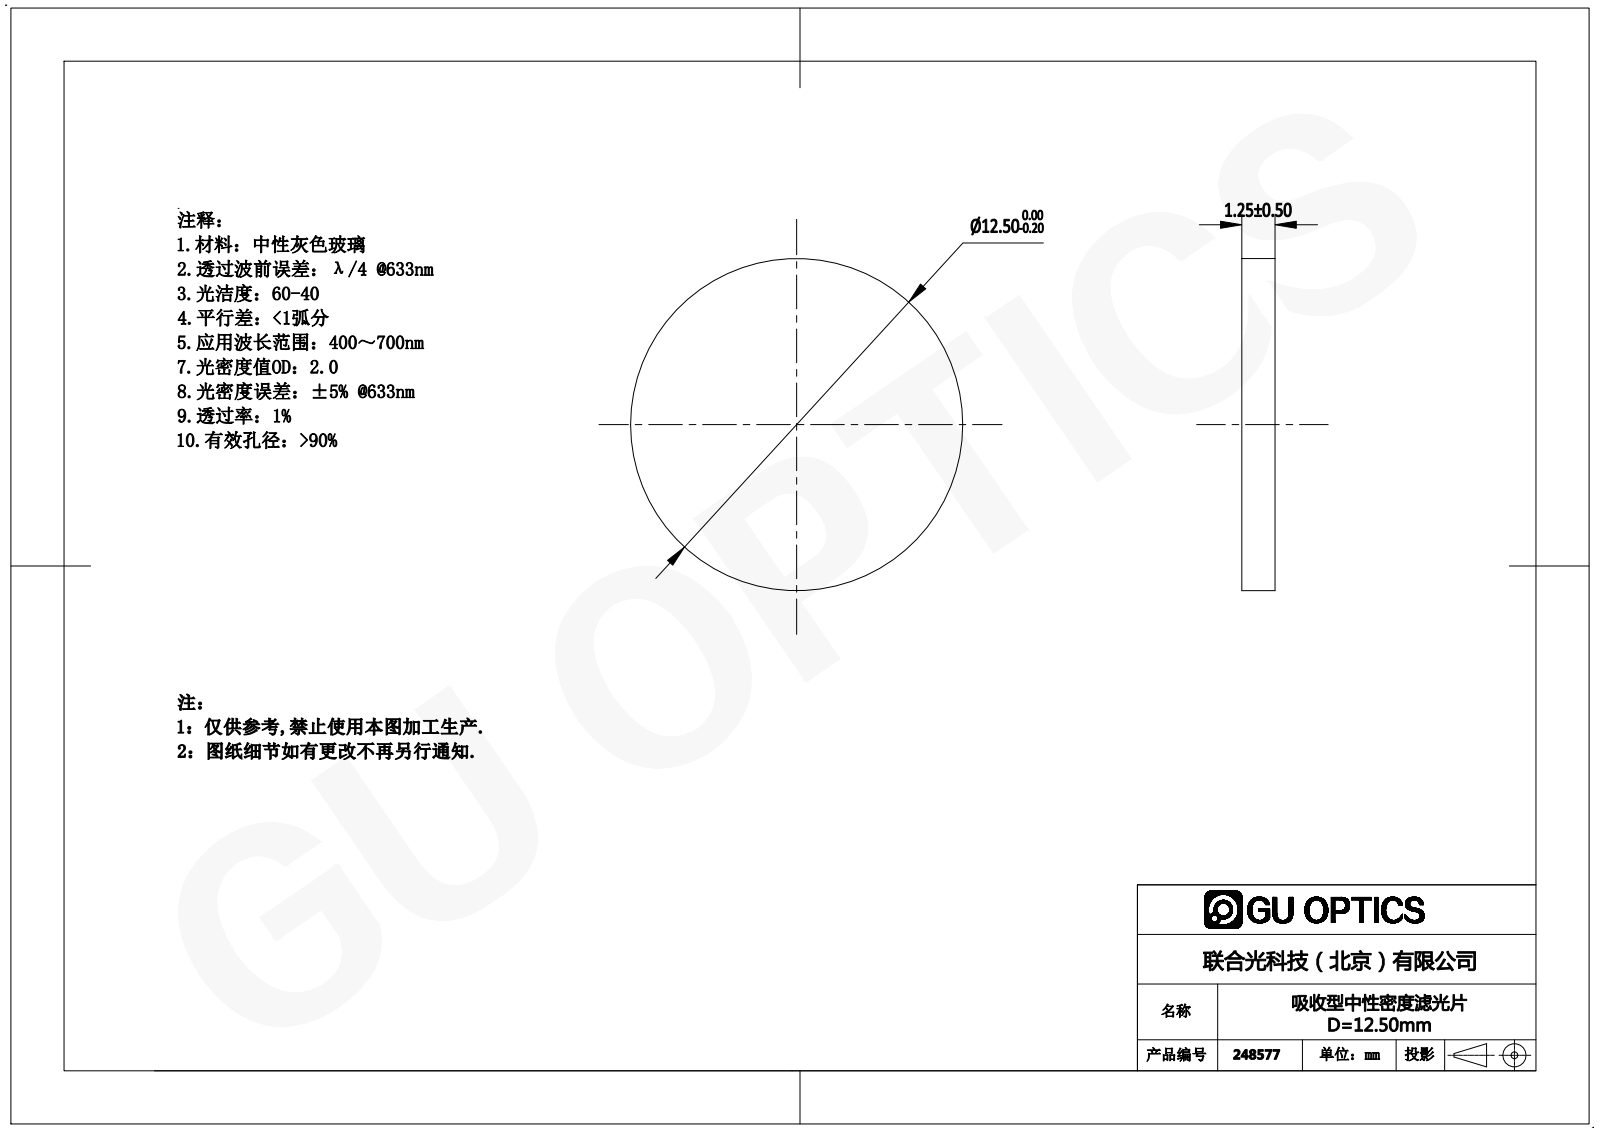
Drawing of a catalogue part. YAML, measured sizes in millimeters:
part_name: "248577"
step_written_by: "SolidWorks 2016 (AUTOMOTIVE_DESIGN)"
units: millimeters
bodies: {solids: 1, faces: 4, planar: 2, cylindrical: 2, other: 0}
overall_size: [12.5, 12.5, 1.25]
volume: 153
surface_area: 295
round_bosses_or_shafts:
  - {diameter: 12.5, count: 1}
face_to_face_distances: [1.25]
